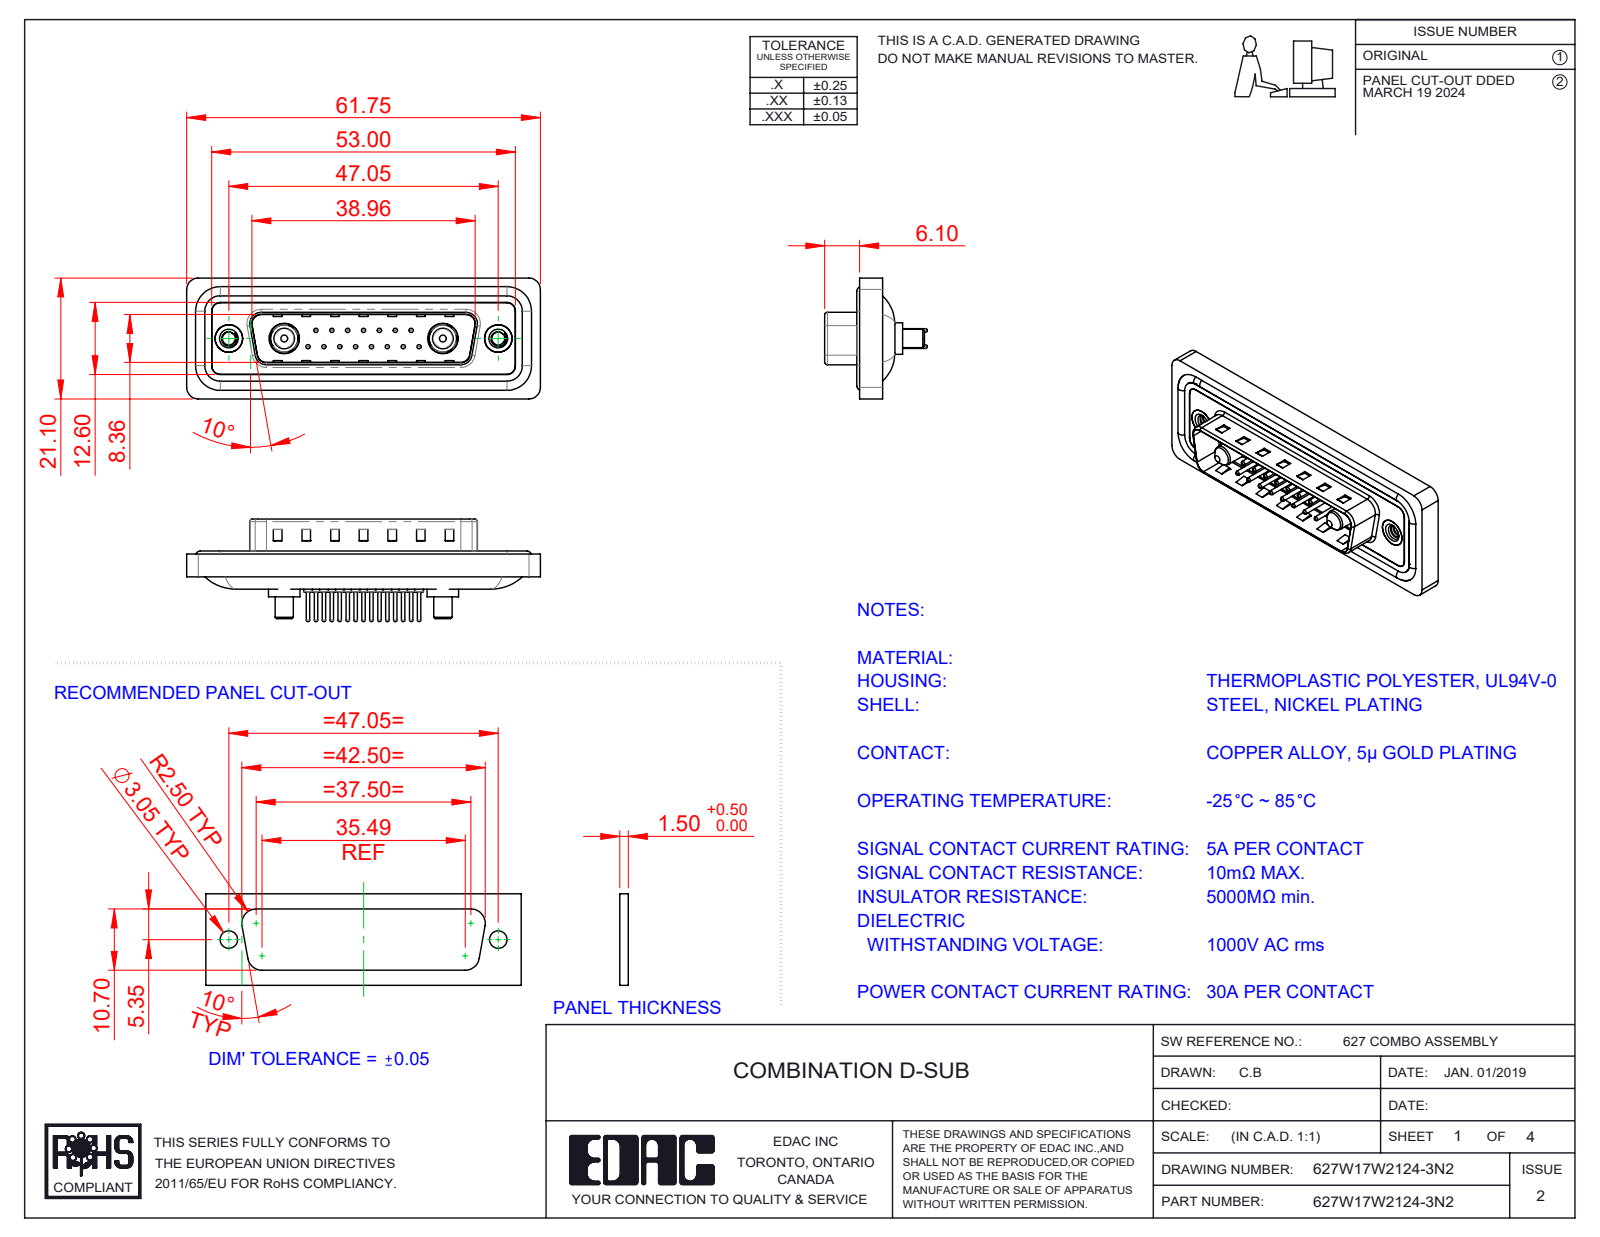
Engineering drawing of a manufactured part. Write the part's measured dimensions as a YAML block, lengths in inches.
part_name: "627Combo Threaded Rivet_2; 627Combo Waterproof Housing_25 Contacts; 627W17W2124-3N2; 627Combo Housing_17W2 (+5 more)"
step_written_by: "SolidWorks 2023 (CONFIG_CONTROL_DESIGN)"
units: inches
bodies: {solids: 26, faces: 1116, planar: 334, cylindrical: 436, other: 346}
overall_size: [2.431, 0.831, 0.705]
volume: 0.444
surface_area: 18.48
round_holes:
  - {diameter: 0.03, count: 15}
  - {diameter: 0.063, count: 15}
  - {diameter: 0.079, count: 15}
  - {diameter: 0.089, count: 2}
  - {diameter: 0.157, count: 2}
  - {diameter: 0.189, count: 2}
  - {diameter: 0.191, count: 2}
  - {diameter: 0.197, count: 2}
  - {diameter: 0.209, count: 2}
round_bosses_or_shafts:
  - {diameter: 0.059, count: 15}
  - {diameter: 0.024, count: 15}
  - {diameter: 0.063, count: 4}
  - {diameter: 0.217, count: 2}
  - {diameter: 0.205, count: 2}
  - {diameter: 0.193, count: 2}
  - {diameter: 0.187, count: 2}
  - {diameter: 0.148, count: 2}
partial_cylinders:
  - {radius: 0.059, count: 22}
  - {radius: 0.079, count: 18}
  - {radius: 0.02, count: 8}
  - {radius: 0.063, count: 8}
  - {radius: 0.01, count: 4}
  - {radius: 0.024, count: 4}
  - {radius: 0.026, count: 4}
  - {radius: 0.035, count: 4}
face_to_face_distances: [0.016, 0.059, 0.043, 0.063, 0.02, 0.122, 0.114, 0.032, 0.377, 0.161]
hole_center_spacings: [0.124, 0.109, 0.218, 0.327, 0.198, 0.295, 0.436, 0.198]
